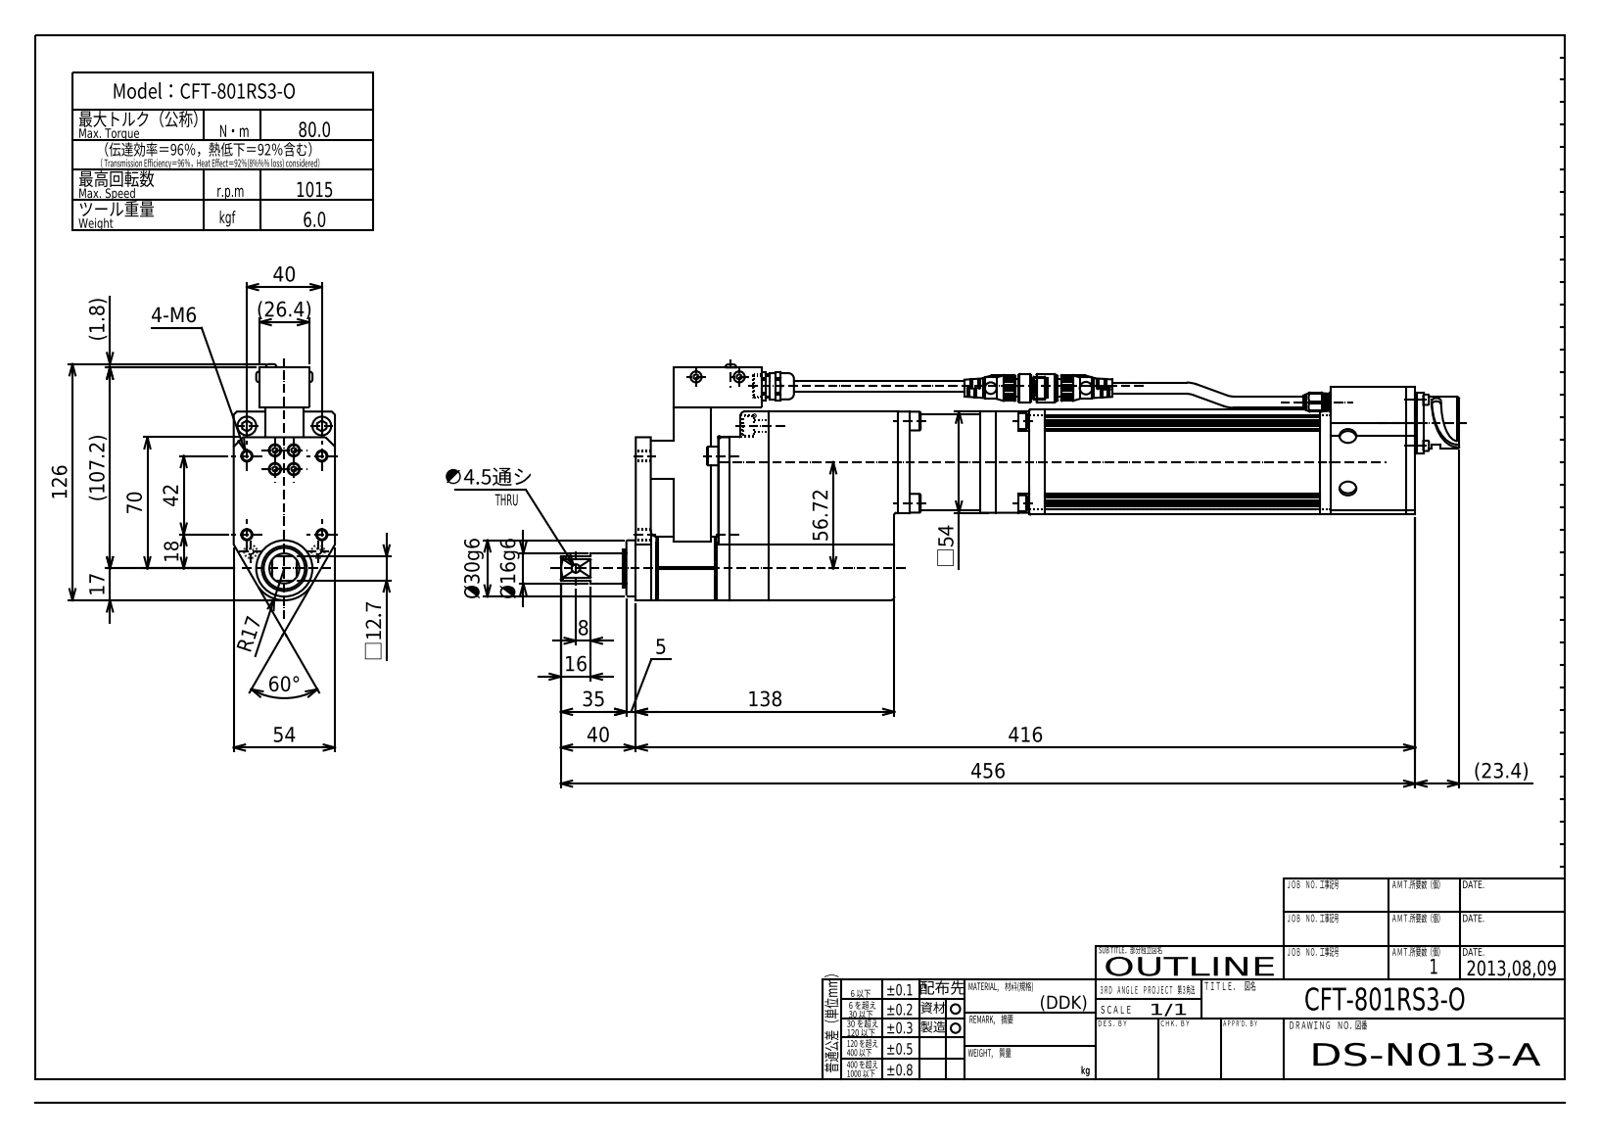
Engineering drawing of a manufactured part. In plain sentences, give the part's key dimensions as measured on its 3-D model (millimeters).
The part is named "CFT-801RS3-O". Its 3-D file was written by "SolidWorks 2013 (CONFIG_CONTROL_DESIGN)". It is 30 solids with 383 faces: 202 planar, 116 cylindrical and 65 other. Overall it measures 480.4 by 125.85 by 54 millimeters. Its volume is 1 243 000 cubic millimeters and its surface area 177 603 square millimeters. Round holes: 4 of diameter 5, 1 of diameter 4.5, 1 of diameter 20.8. Round bosses or shafts: 8 of diameter 10, 4 of diameter 8.5, 3 of diameter 5.9, 1 of diameter 51, 1 of diameter 34, 1 of diameter 30, 1 of diameter 28, 1 of diameter 27.4. Partial cylindrical surfaces (rounded edges, fillets, slot ends): 4 of radius 0.5, 4 of radius 1, 2 of radius 9, 2 of radius 12, 1 of radius 24.5, 1 of radius 28, 1 of radius 42. The main face-to-face distances are 54, 17, 8, 323, 153, 6, 212, 52, 75, 92. The hole center spacings are 26.71, 40, 42, 58, 62.96.
